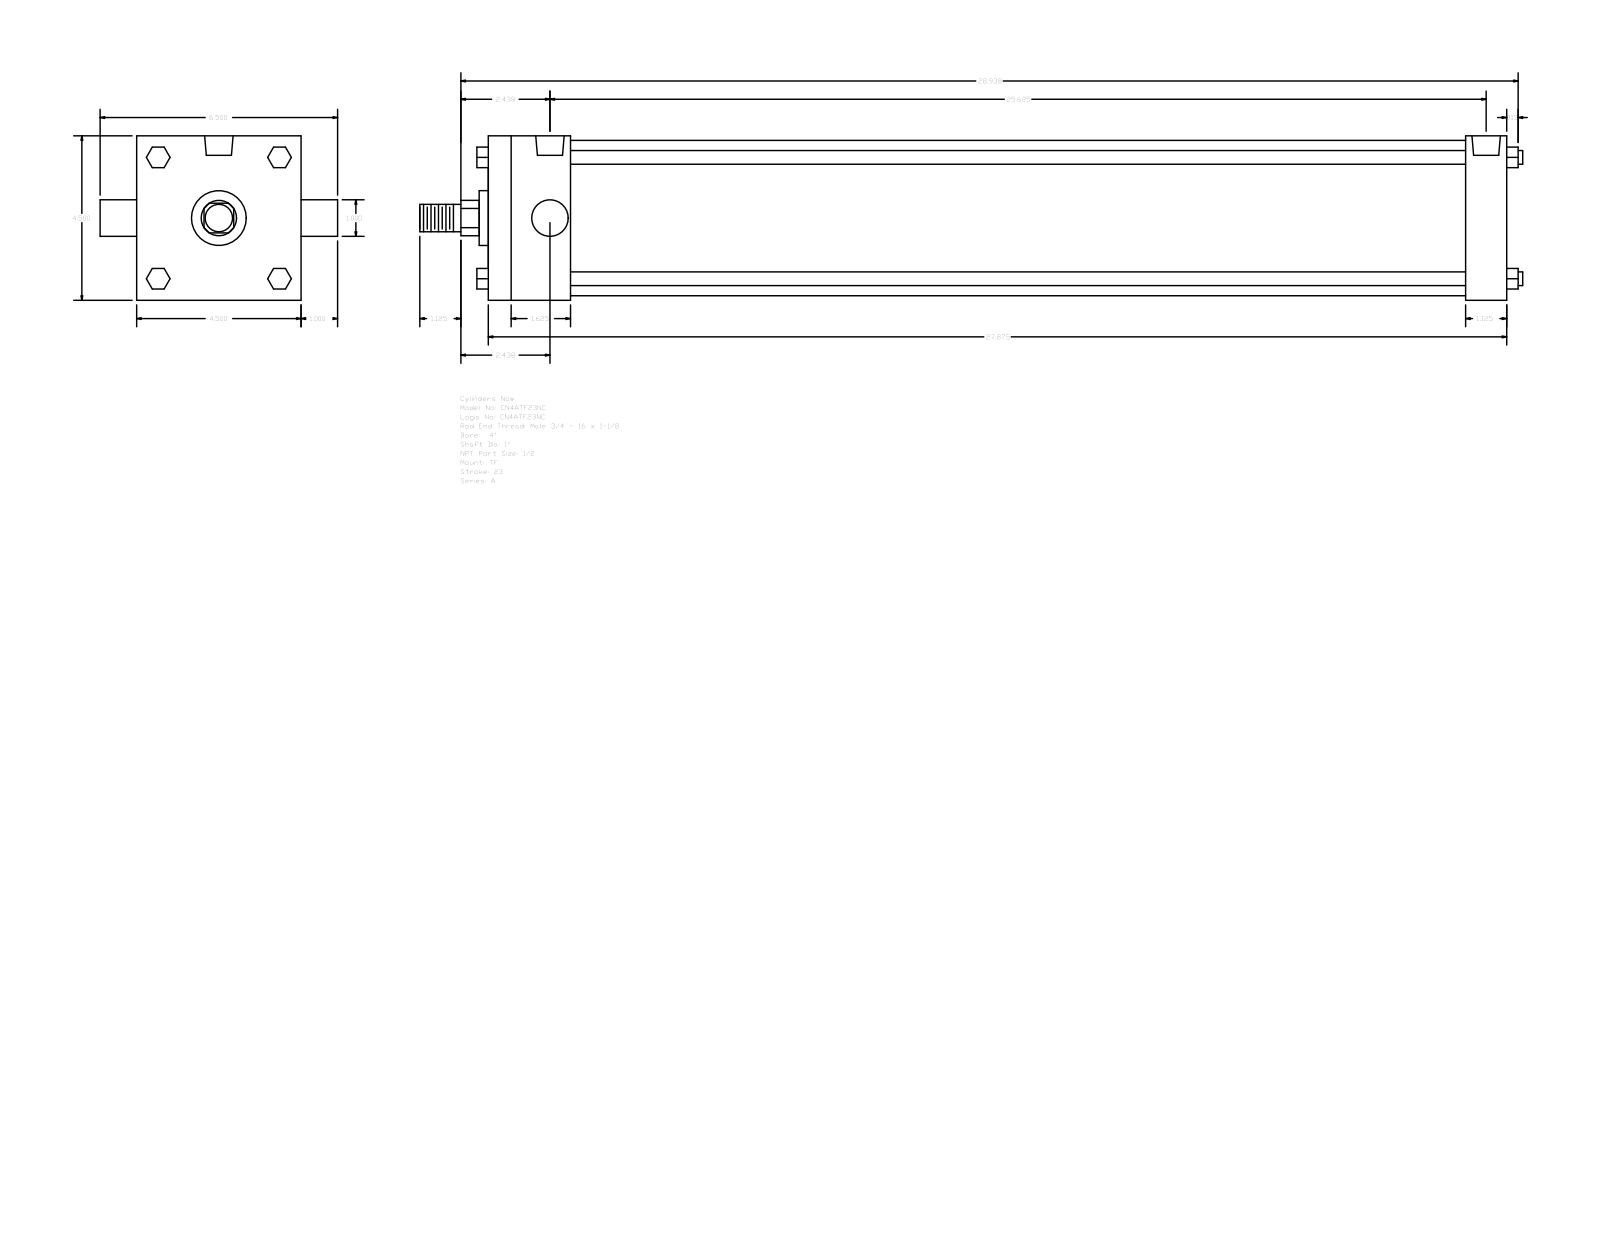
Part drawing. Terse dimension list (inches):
name: A_TF__0400_1
written by: GSSL Pune (CONFIG_CONTROL_DESIGN)
unit: in
bodies: 0 solids, 120 faces (92 planar, 28 cylindrical, 0 other)
size: 30.187 × 6.5 × 4.5
holes: 3× ⌀0.344, 2× ⌀0.778
bosses: 4× ⌀0.375, 2× ⌀1, 1× ⌀4.25, 1× ⌀1.5, 1× ⌀0.75
rounds: 1× R0.484
face distances: 4.5, 27.875, 26.75, 1.125, 2.25, 24.5, 25.625, 0.563, 1.66, 2.875
hole spacings: 0.125, 25.5, 25.375, 25.625
